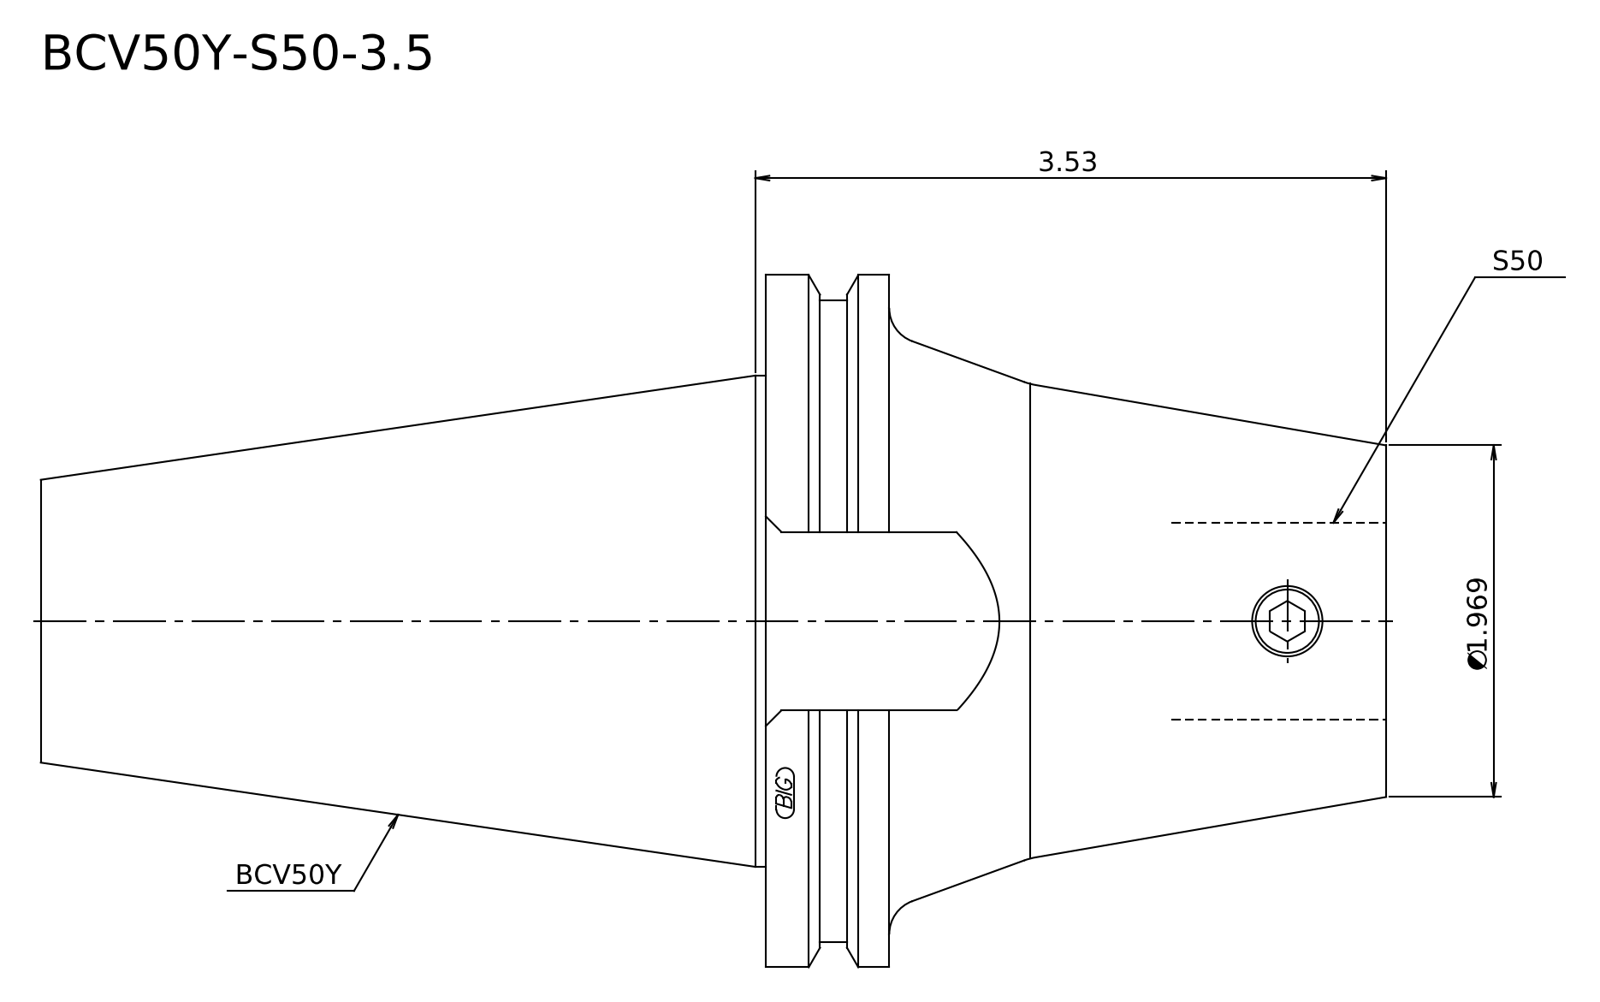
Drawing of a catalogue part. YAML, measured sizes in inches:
step_written_by: "Kubotek KeyCreator 2011 V10.0.2 (22737) (automotive_design)"
units: inches
bodies: {solids: 1, faces: 16, planar: 6, cylindrical: 4, other: 6}
overall_size: [7.531, 3.875, 3.875]
volume: 37.18
surface_area: 74.9
round_bosses_or_shafts:
  - {diameter: 3.875, count: 1}
  - {diameter: 3.594, count: 1}
  - {diameter: 2.75, count: 1}
face_to_face_distances: [3.472, 2.781, 0.691, 7.531, 4.75, 4.059, 3.169, 0.388, 0.303, 4.362]
